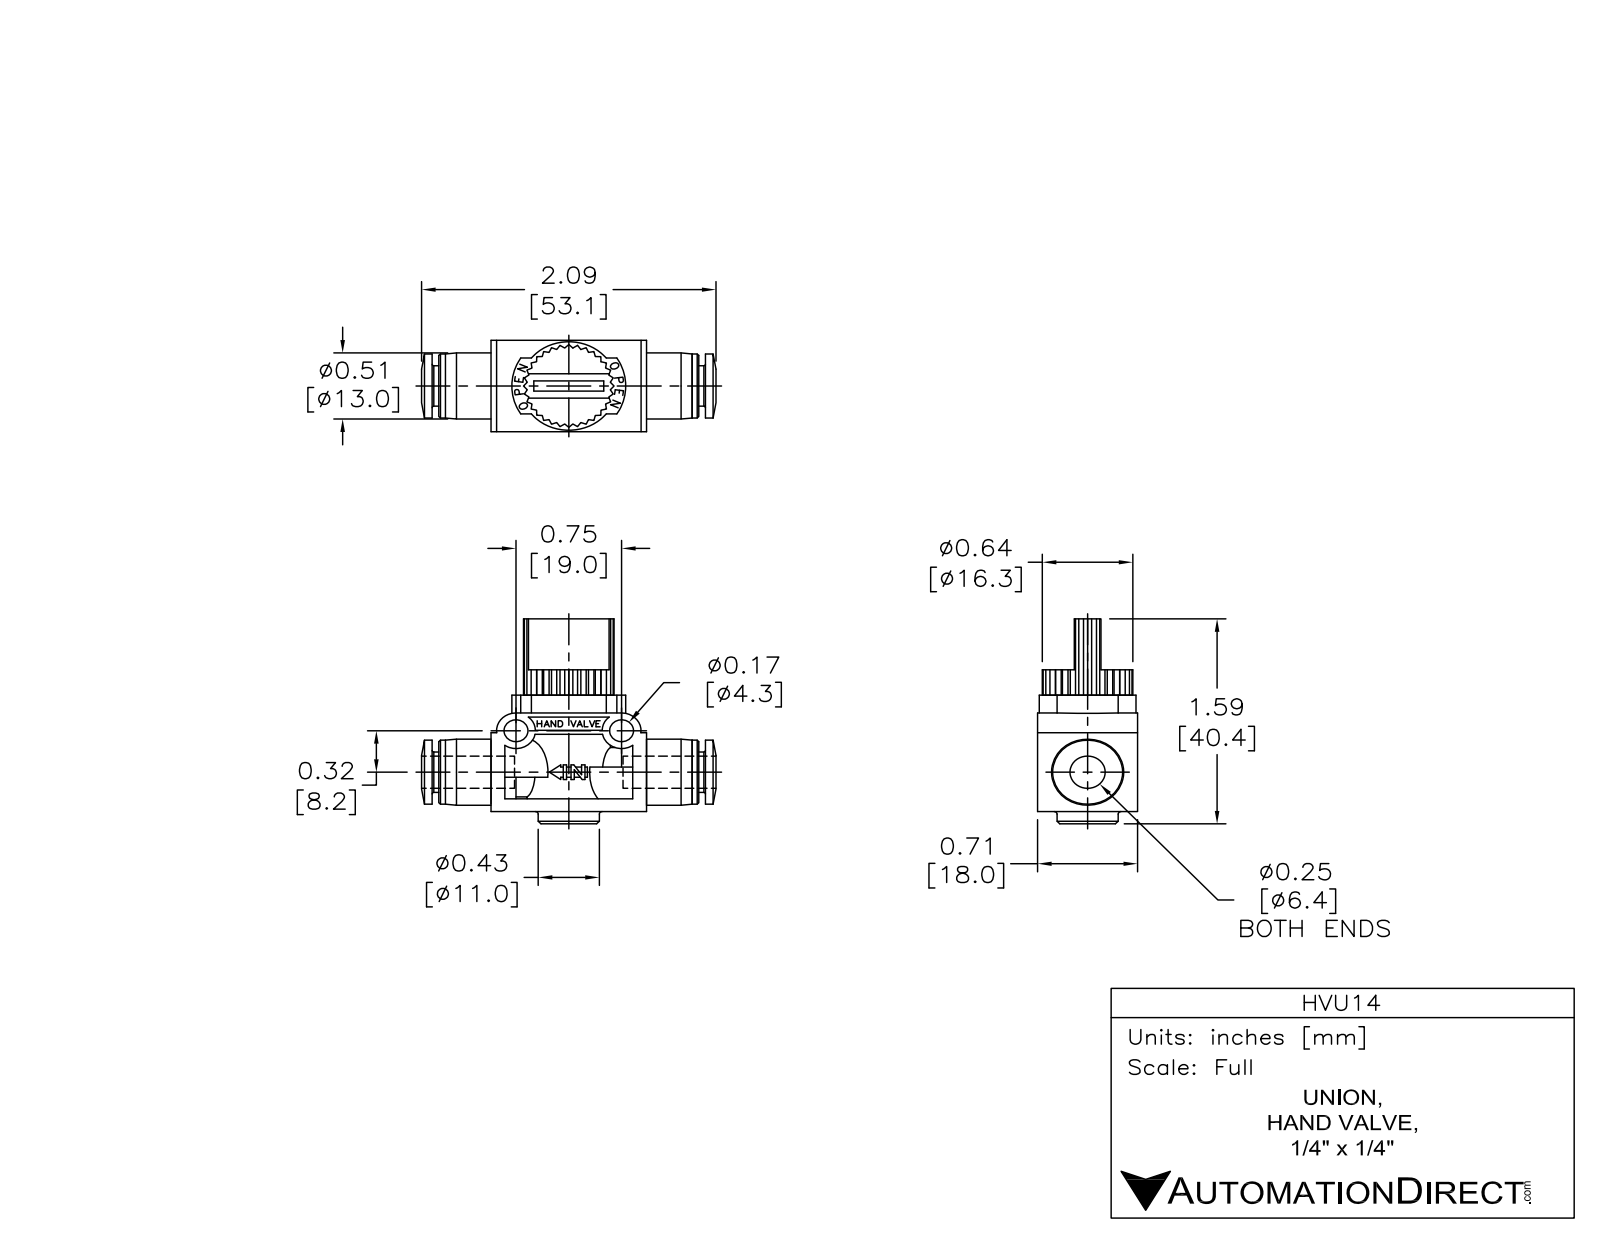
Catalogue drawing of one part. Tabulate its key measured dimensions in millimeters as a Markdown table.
| quantity | value |
| --- | --- |
| part name | HVU14 |
| STEP written by | SolidWorks 2015 (AUTOMOTIVE_DESIGN) |
| units | millimeters |
| bodies | 1 solid, 286 faces (173 planar, 77 cylindrical, 36 other) |
| overall size | 53 × 40.3 × 18 |
| volume | 11 900 mm³ |
| surface area | 7 129 mm² |
| round holes (diameter × count) | 4.3 × 2, 6.6 × 1 |
| round bosses / shafts (diameter × count) | 15 × 1, 13 × 1, 12.6 × 1, 11 × 1, 8 × 1 |
| partial cylindrical surfaces (radius × count) | 3.5 × 2, 4.8 × 1, 5.5 × 1, 7.7 × 1, 7.9 × 1, 8.7 × 1, 10.3 × 1 |
| main face-to-face distances | 2.5, 6.6, 11.4, 1.4, 3.4, 10, 8, 11.9, 18, 11.9 |
| hole center spacings | 19 |
